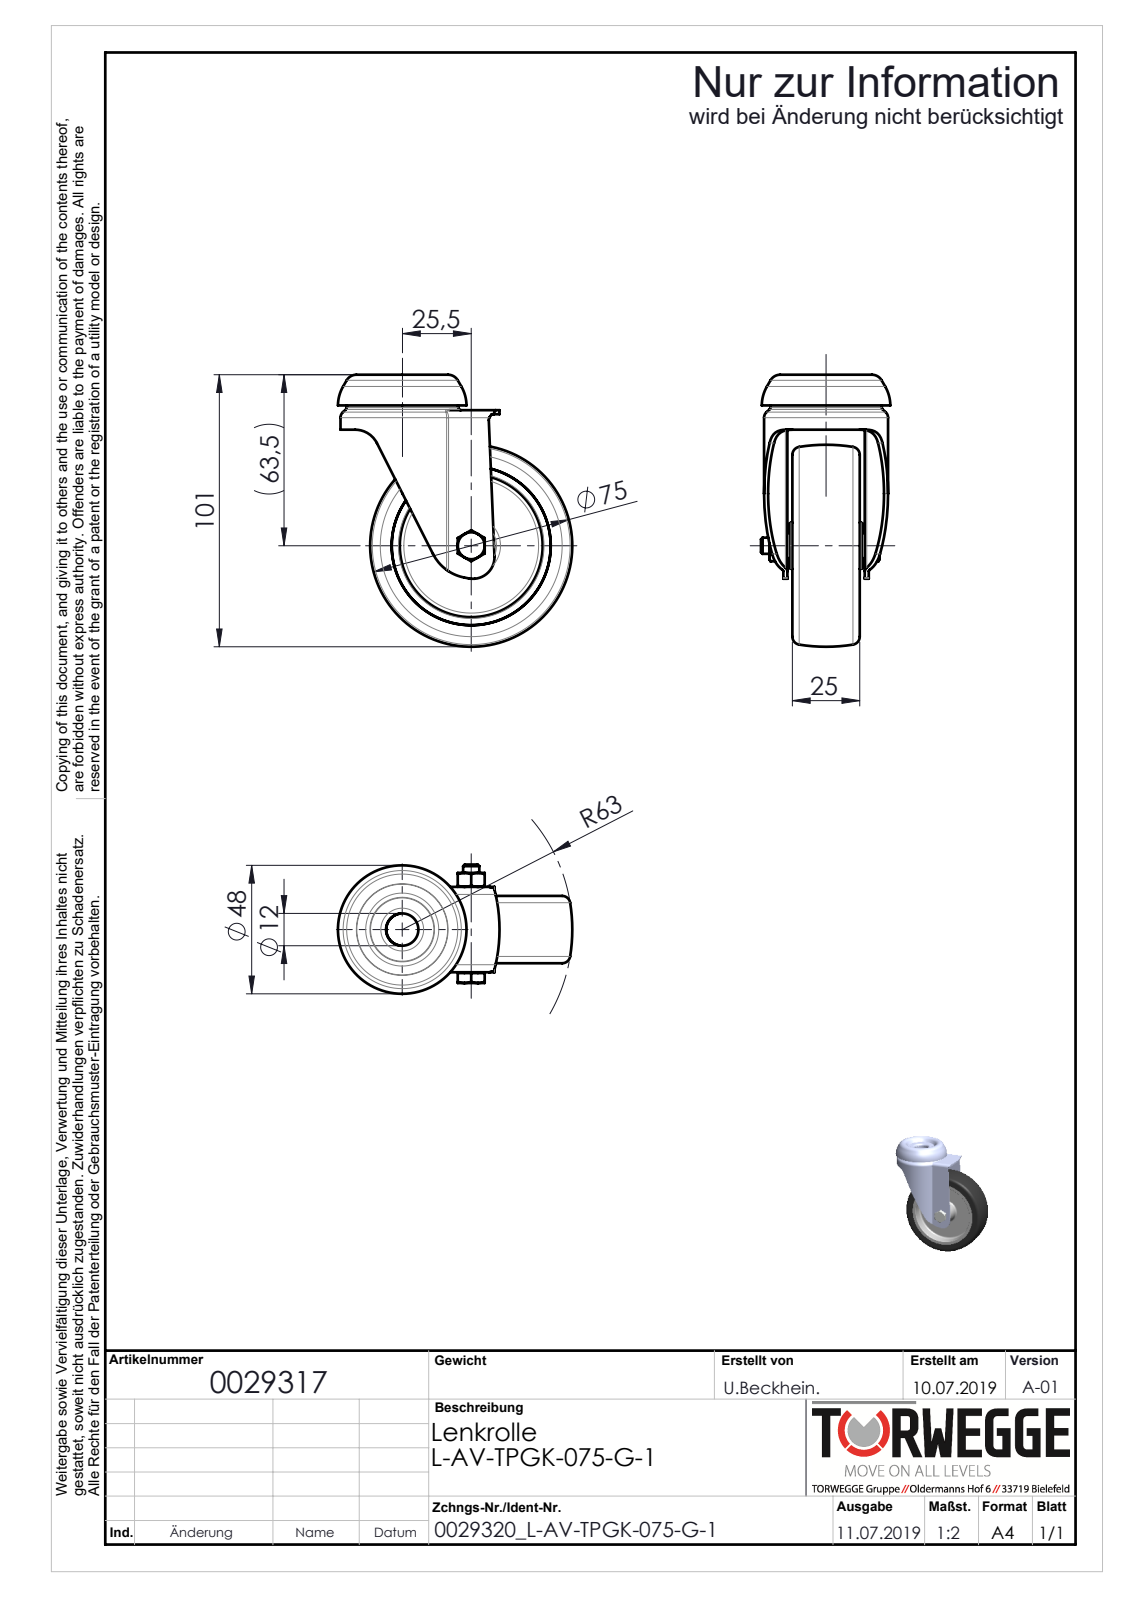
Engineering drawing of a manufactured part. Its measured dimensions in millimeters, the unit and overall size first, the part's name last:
Units: millimetres
Overall size (bounding box): 101 × 86.95 × 48
Round holes (diameter × count): ⌀12.03 ×1, ⌀53 ×1, ⌀59 ×1
Round bosses / shafts (diameter × count): ⌀10 ×1, ⌀6 ×1
Partial cylindrical surfaces — rounded edges, fillets, slot ends (radius × count): R1 ×2, R1.3 ×2, R2.5 ×2, R2.8 ×2, R2 ×1, R8 ×1, R9 ×1, R16.5 ×1
Main face-to-face distances: 10, 15, 1.5, 1.85, 11.85, 16.85, 26.85, 3.35, 13.35, 18.35
Bodies: 0 solids, 173 faces (42 planar, 43 cylindrical, 88 other)
Part name (STEP PRODUCT): 0029317_L-AV-TPGK-075-G-1_(A-01)
STEP written by: SolidWorks 2018 (AUTOMOTIVE_DESIGN)
